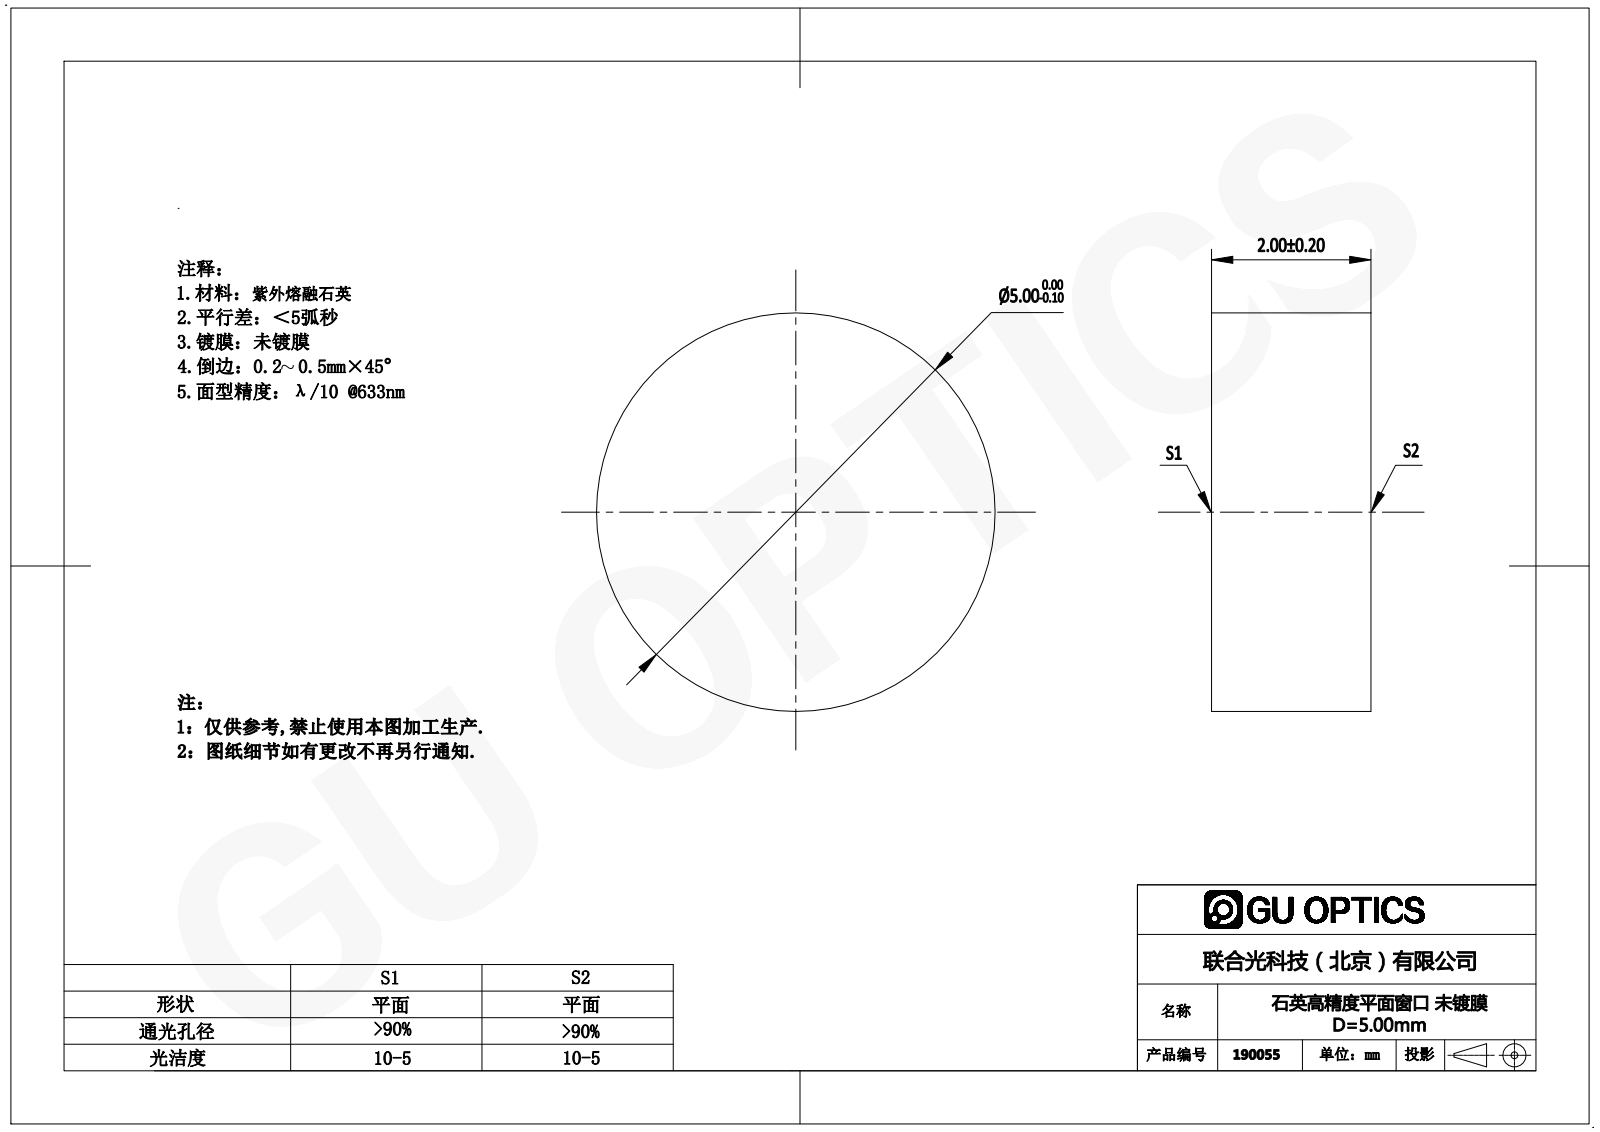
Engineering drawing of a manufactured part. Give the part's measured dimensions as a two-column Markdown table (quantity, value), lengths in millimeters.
| quantity | value |
| --- | --- |
| part name | 190055 |
| STEP written by | SolidWorks 2016 (AUTOMOTIVE_DESIGN) |
| units | millimeters |
| bodies | 1 solid, 4 faces (2 planar, 2 cylindrical, 0 other) |
| overall size | 5 × 5 × 2 |
| volume | 39 mm³ |
| surface area | 71 mm² |
| round bosses / shafts (diameter × count) | 5 × 1 |
| main face-to-face distances | 2 |
